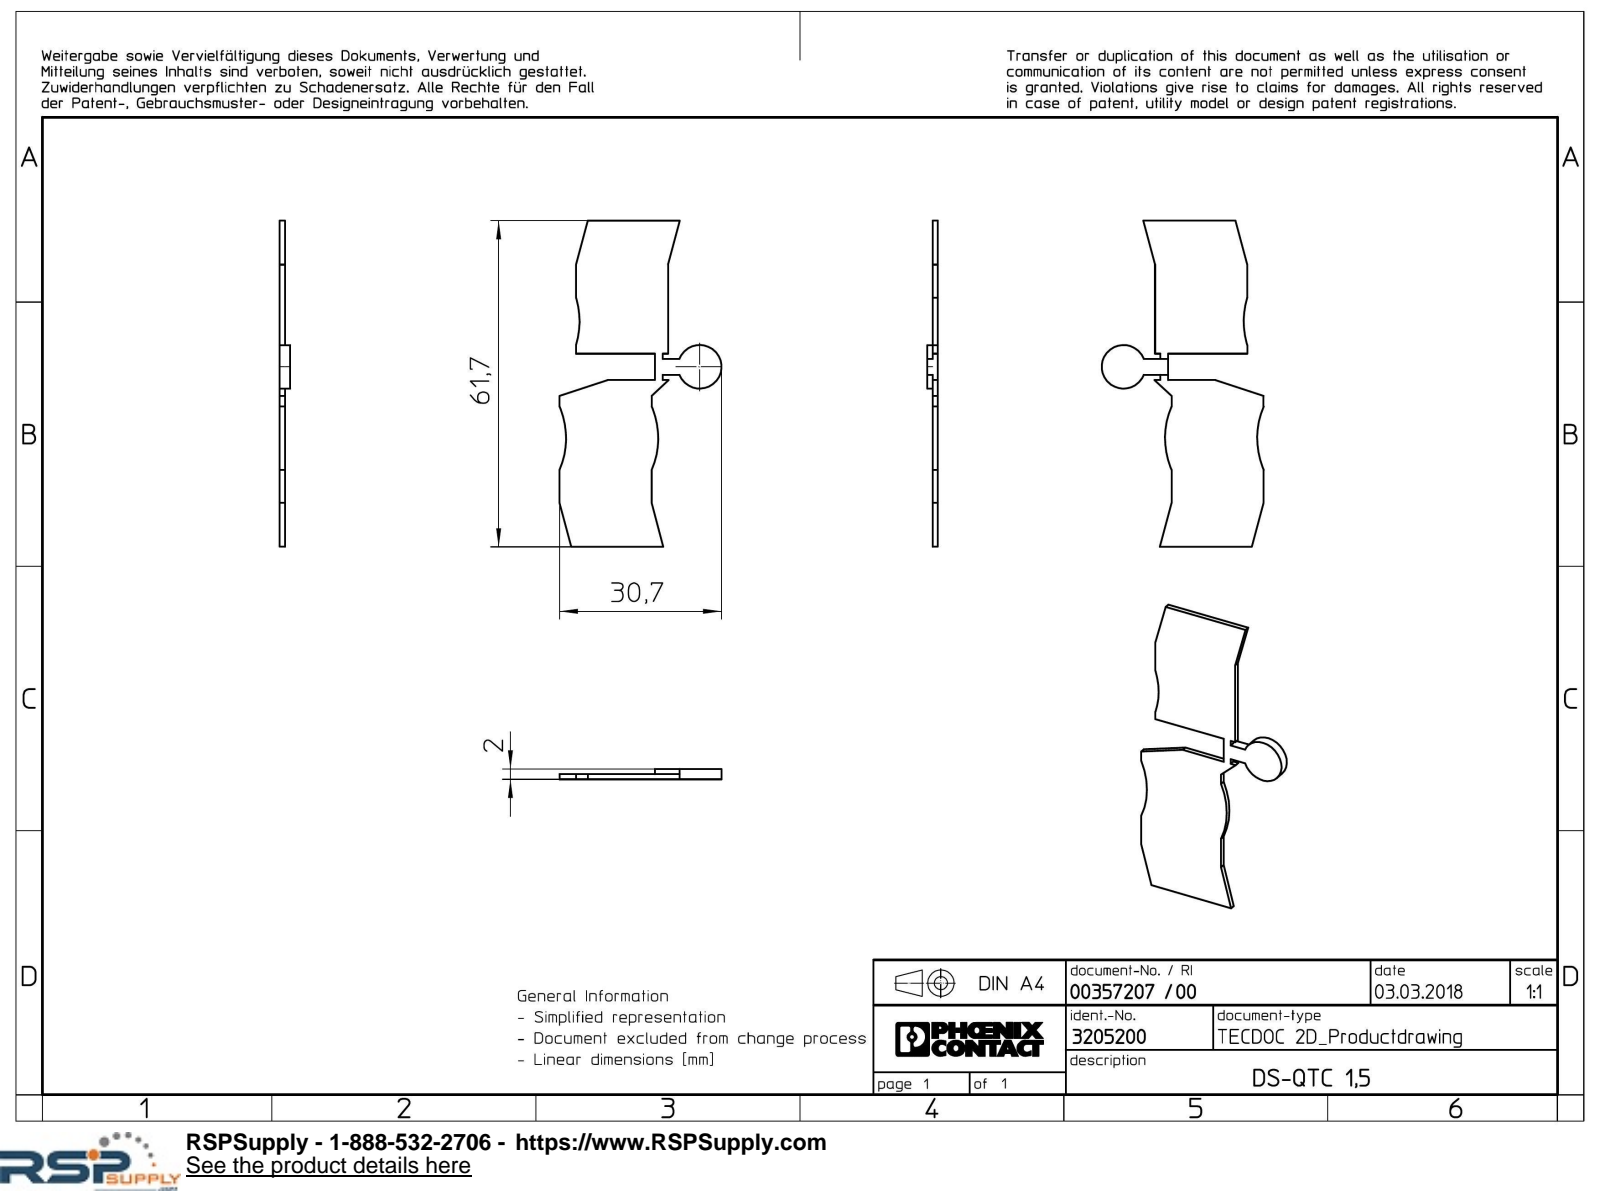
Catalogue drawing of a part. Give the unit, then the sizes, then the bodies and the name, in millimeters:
Units: millimetres
Overall size (bounding box): 61.7 × 30.7 × 2
Round bosses / shafts (diameter × count): ⌀8.25 ×1
Partial cylindrical surfaces — rounded edges, fillets, slot ends (radius × count): R15 ×3
Main face-to-face distances: 1, 2, 61.7, 16.86, 3.12, 17.45, 25.15, 36.55, 4, 30.15
Volume: 1 113 mm³ · Surface area: 2 348 mm²
Bodies: 1 solid, 32 faces (28 planar, 4 cylindrical, 0 other)
Part name (STEP PRODUCT): DS-QTC_1.5-select
STEP written by: Creo Elements/Direct Modeling 18.1I 14-Aug-2016 (C) Parametric Technology GmbH (AUTOMOTIVE_DESIGN)
